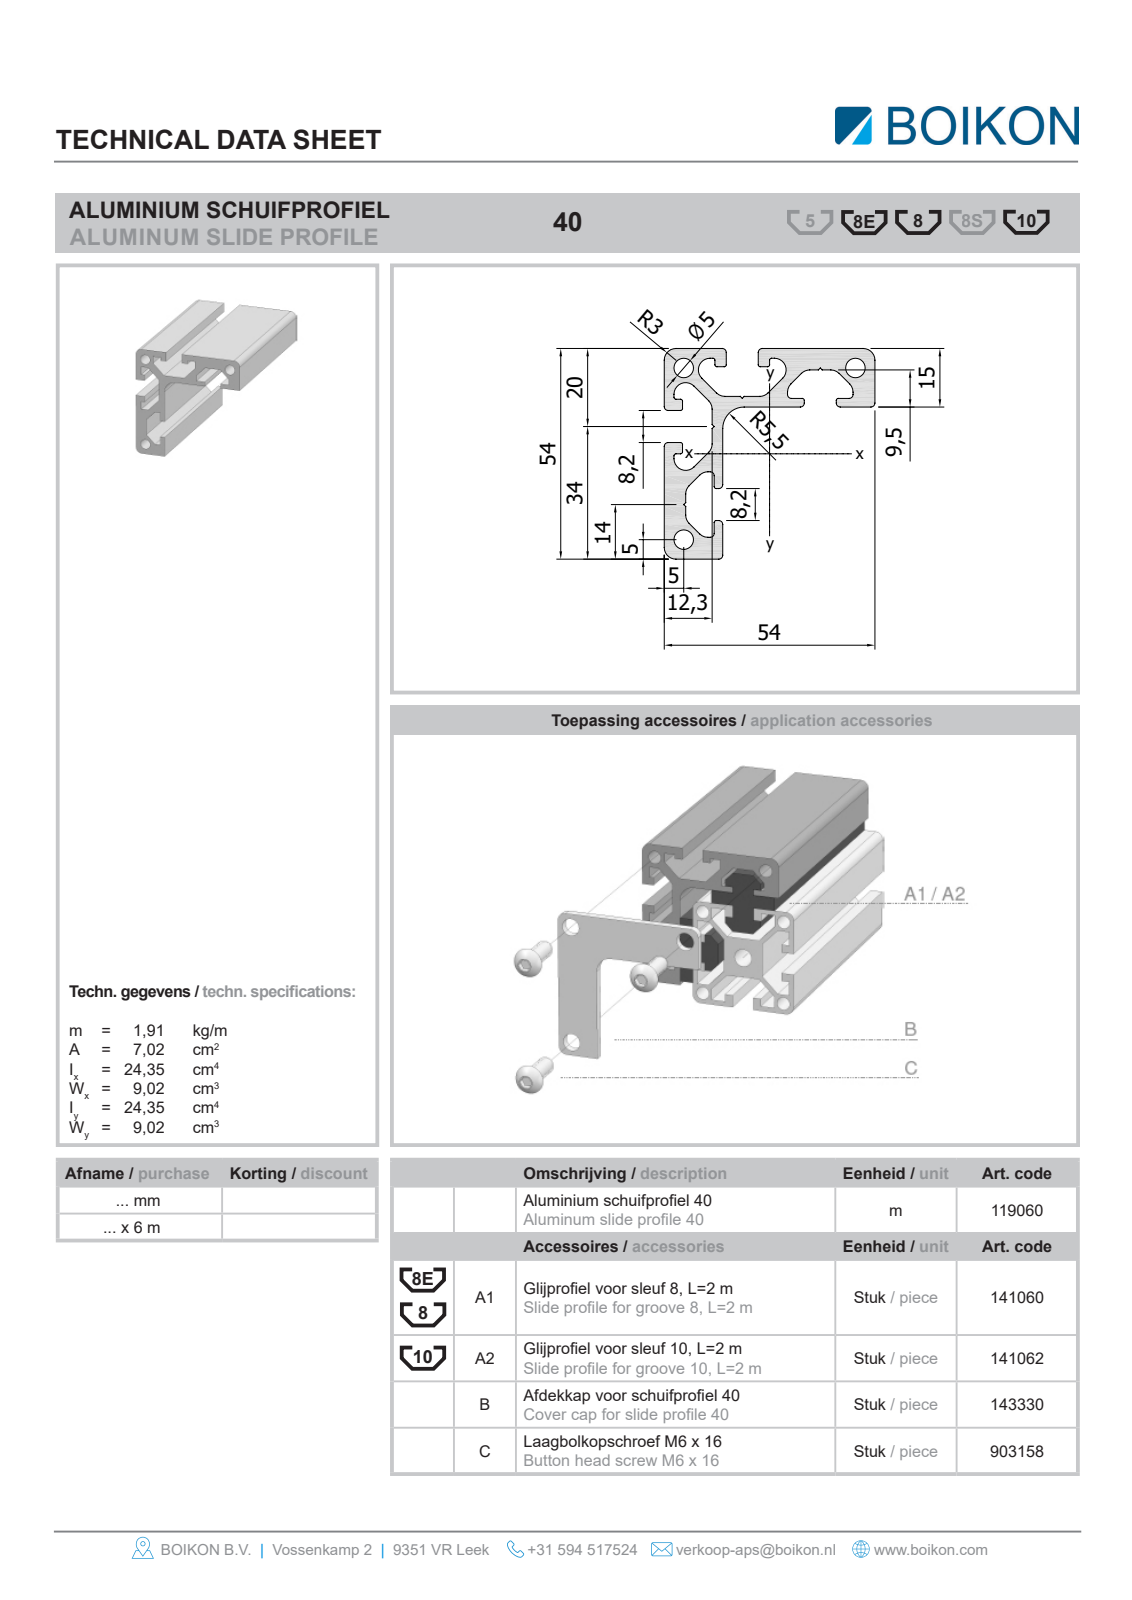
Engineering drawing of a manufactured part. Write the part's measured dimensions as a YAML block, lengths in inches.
part_name: "Root; 119060Alu Schuifprofiel 40BOIKON0"
step_written_by: "HiCAD 2013 1802.4 Build 509 (AUTOMOTIVE_DESIGN)"
units: inches
bodies: {solids: 1, faces: 63, planar: 56, cylindrical: 7, other: 0}
overall_size: [39.37, 2.126, 2.126]
volume: 44.32
surface_area: 656.2
round_holes:
  - {diameter: 0.197, count: 3}
partial_cylinders:
  - {radius: 0.118, count: 3}
  - {radius: 0.217, count: 1}
face_to_face_distances: [0.591, 0.114, 0.476, 2.126, 1.535, 1.622, 1.65, 0.39, 0.177, 0.504]
hole_center_spacings: [1.732, 2.45]
